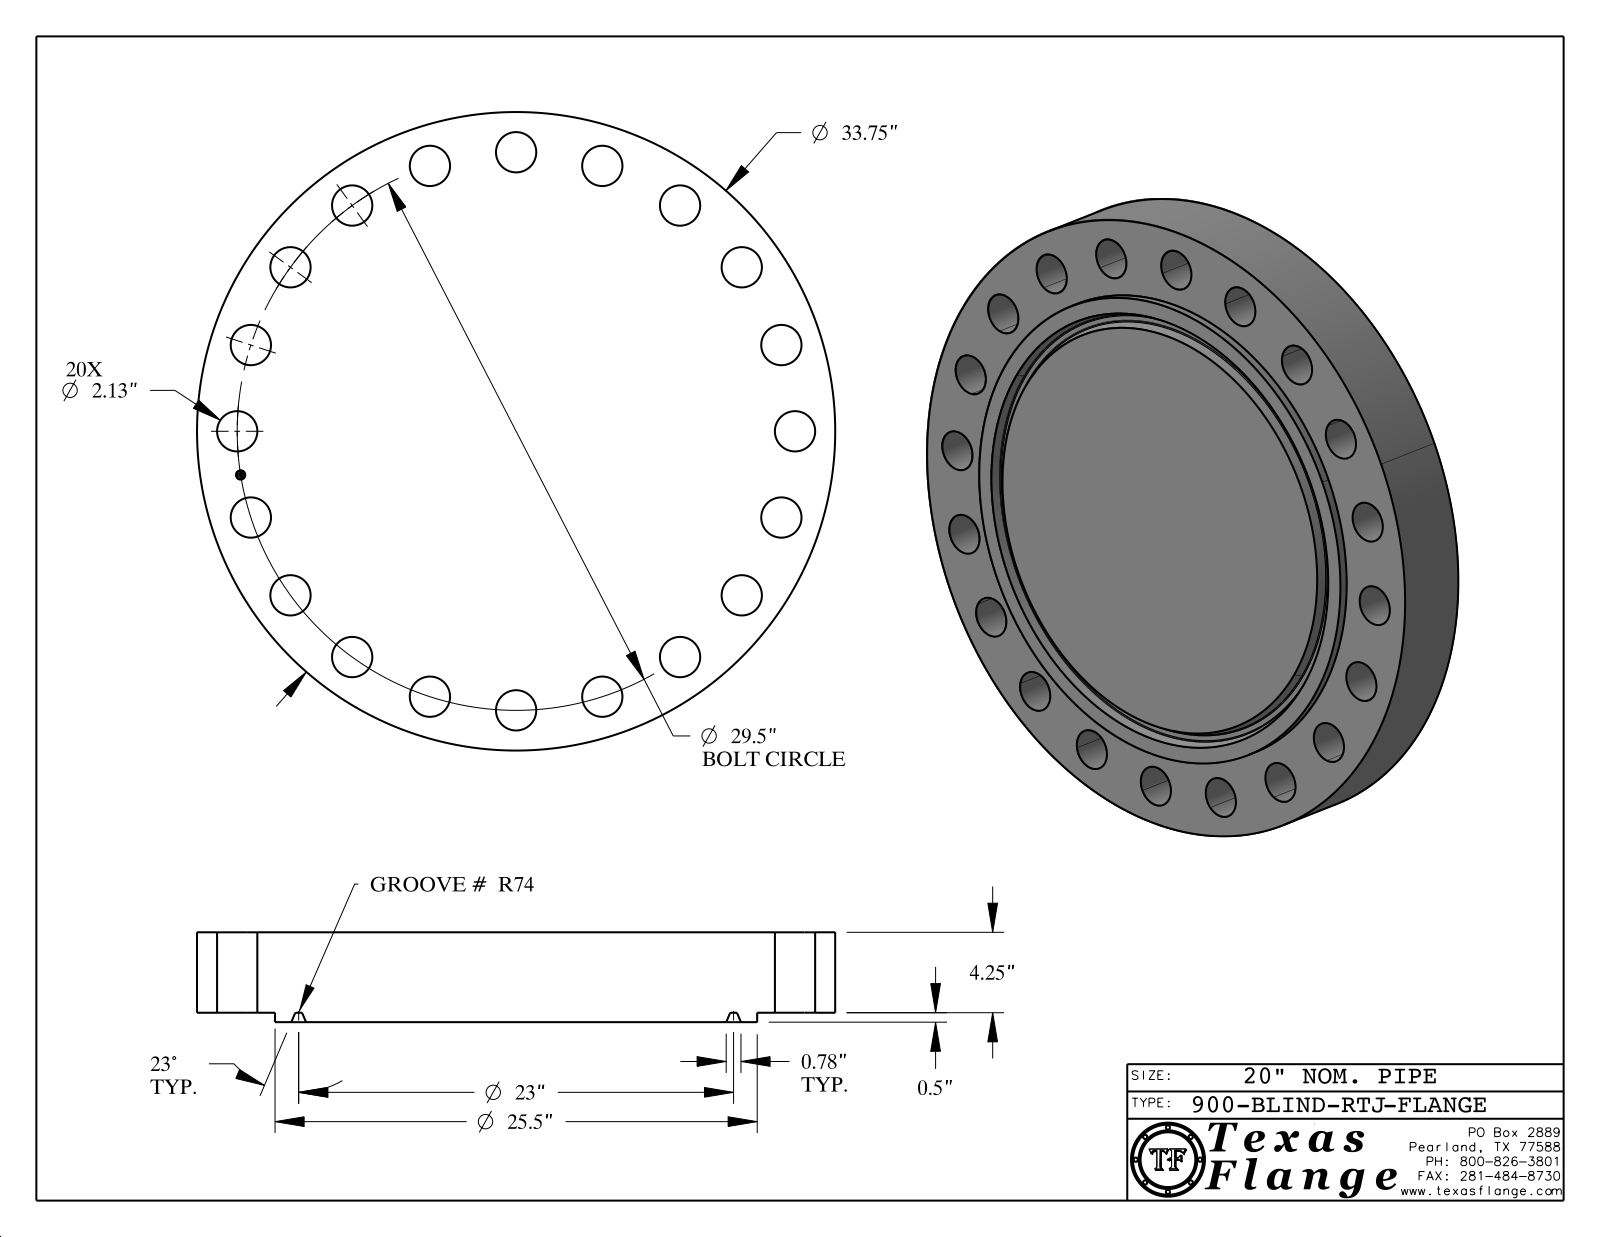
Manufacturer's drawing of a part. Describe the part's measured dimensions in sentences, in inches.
The part is named "900-BLIND-RTJ". Its 3-D file was written by "CATIA V5 STEP AP214 (AUTOMOTIVE_DESIGN)". It is 1 solid with 442 faces: 370 planar, 64 cylindrical and 8 other. Overall it measures 33.75 by 33.75 by 4.75 inches. Its volume is 3 734 cubic inches and its surface area 2 753 square inches. Round holes: 20 of diameter 2.13, 1 of diameter 0.495. Round bosses or shafts: 8 of diameter 0.03, 1 of diameter 33.75, 1 of diameter 25.5, 1 of diameter 0.39. The main face-to-face distances are 4.75, 0.5, 4.25, 4.735, 4.235, 0.015, 0.148, 0.145, 0.027, 0.096. The hole center spacings are 29.137, 4.615, 17.34, 20.859, 23.866, 26.285, 9.116, 13.393.
